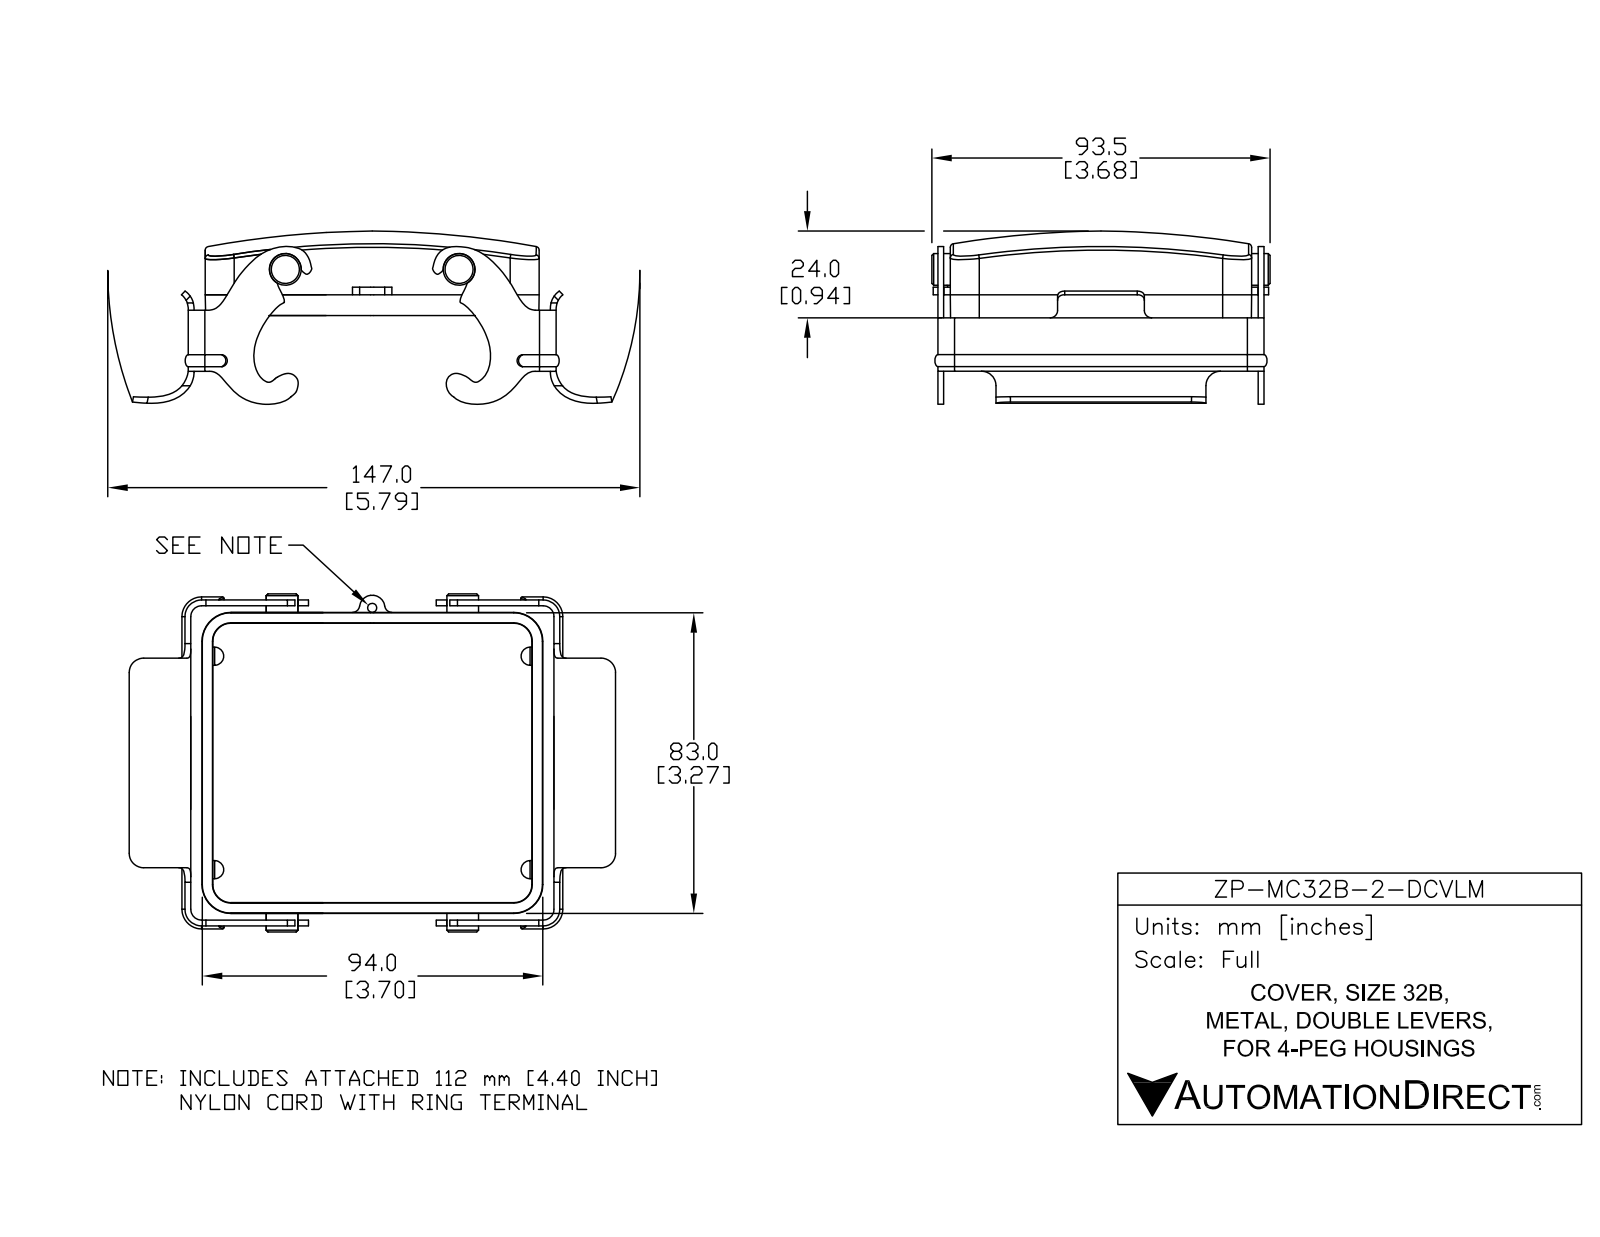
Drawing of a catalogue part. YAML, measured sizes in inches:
part_name: "ZP-MC32B-2-DCVLM"
step_written_by: "SolidWorks 2014 (AUTOMOTIVE_DESIGN)"
units: inches
bodies: {solids: 5, faces: 305, planar: 136, cylindrical: 88, other: 81}
overall_size: [7.601, 5.215, 2.626]
volume: 4.248
surface_area: 88
round_holes:
  - {diameter: 0.098, count: 1}
  - {diameter: 0.161, count: 1}
round_bosses_or_shafts:
  - {diameter: 0.344, count: 2}
partial_cylinders:
  - {radius: 0.079, count: 8}
  - {radius: 0.157, count: 6}
  - {radius: 0.197, count: 5}
  - {radius: 0.315, count: 5}
  - {radius: 0.018, count: 4}
  - {radius: 0.098, count: 4}
  - {radius: 0.118, count: 4}
  - {radius: 0.181, count: 4}
face_to_face_distances: [0.063, 3.159, 0.118, 3.484, 3.514, 0.253, 3.294, 0.19, 3.231, 0.135]
